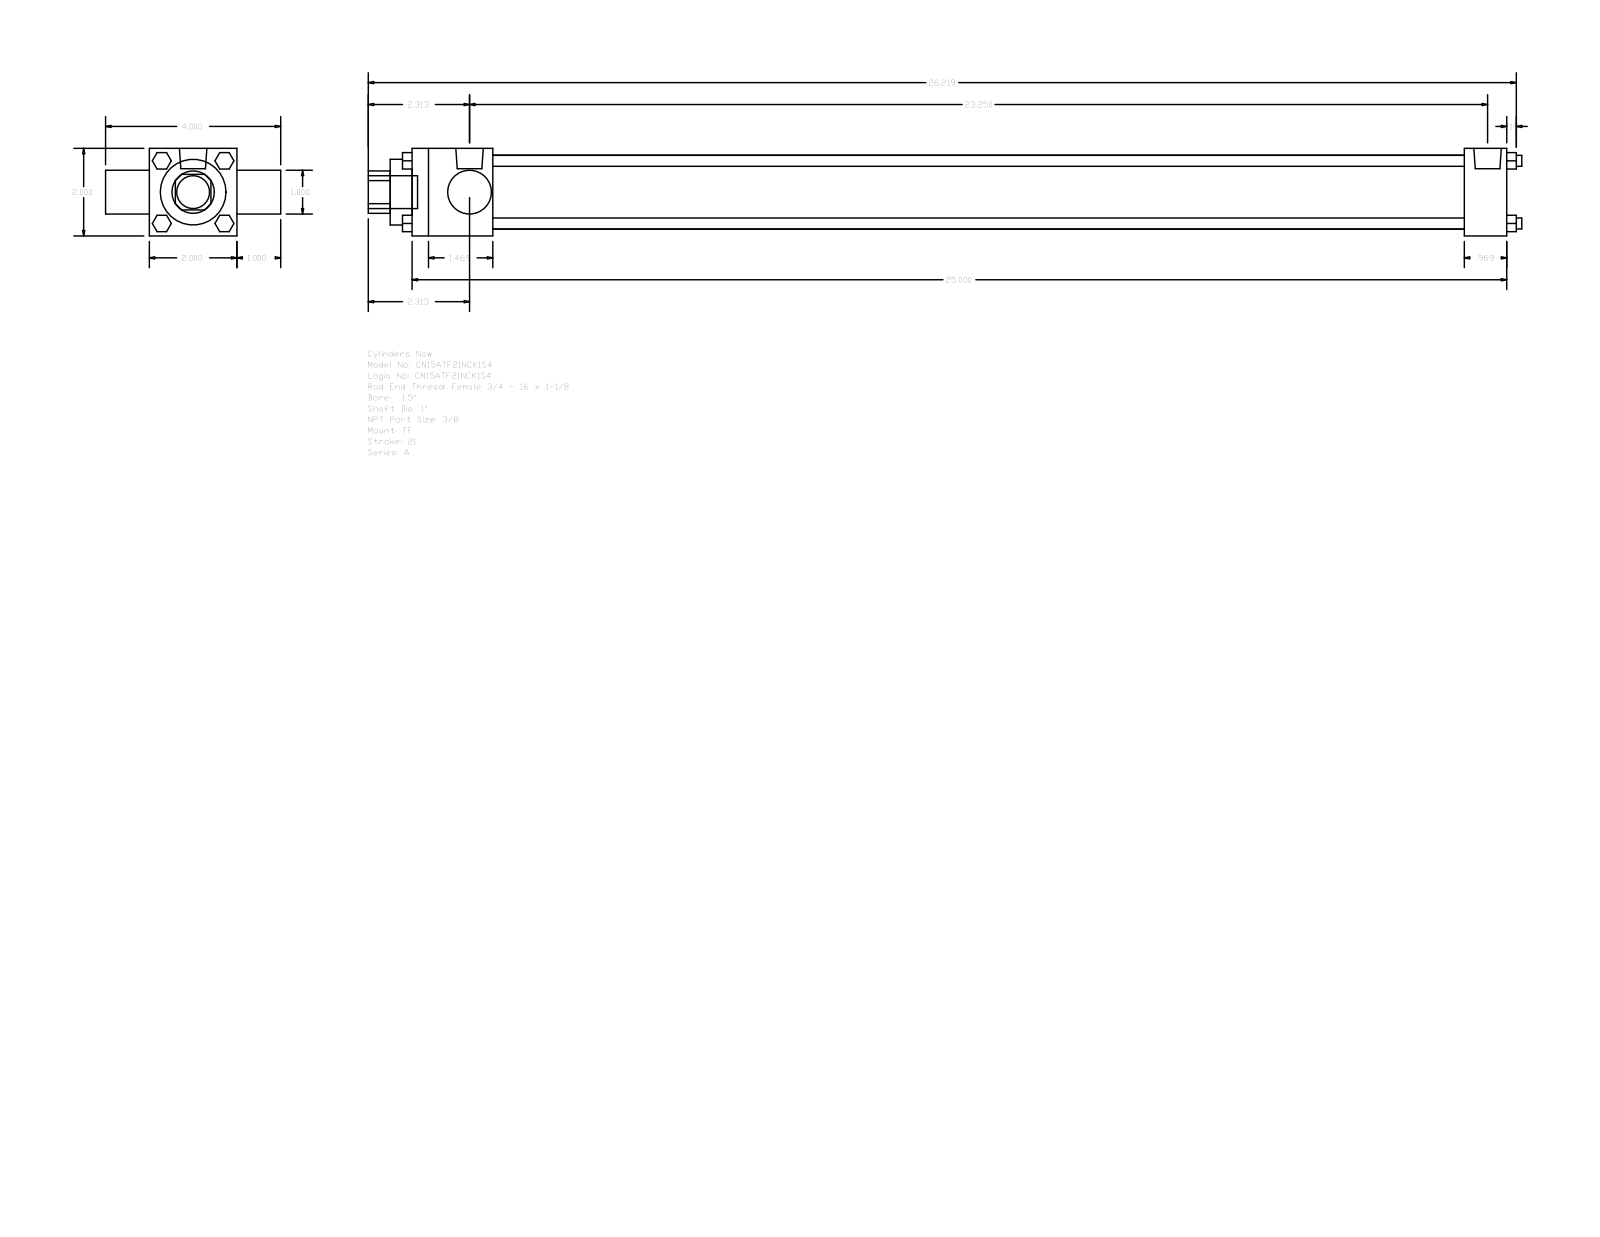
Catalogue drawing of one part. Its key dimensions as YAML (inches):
part_name: "A_TF__0150_1"
step_written_by: "GSSL Pune (CONFIG_CONTROL_DESIGN)"
units: inches
bodies: {solids: 0, faces: 120, planar: 92, cylindrical: 28, other: 0}
overall_size: [26.344, 4, 2]
round_holes:
  - {diameter: 1, count: 2}
  - {diameter: 1.5, count: 1}
  - {diameter: 1.69, count: 1}
round_bosses_or_shafts:
  - {diameter: 0.25, count: 4}
  - {diameter: 0.219, count: 3}
  - {diameter: 0.627, count: 2}
  - {diameter: 0.75, count: 1}
partial_cylinders:
  - {radius: 0.484, count: 1}
face_to_face_distances: [2, 1, 25, 3, 1.844, 24.031, 22.187, 23.156, 0.969, 0.5]
